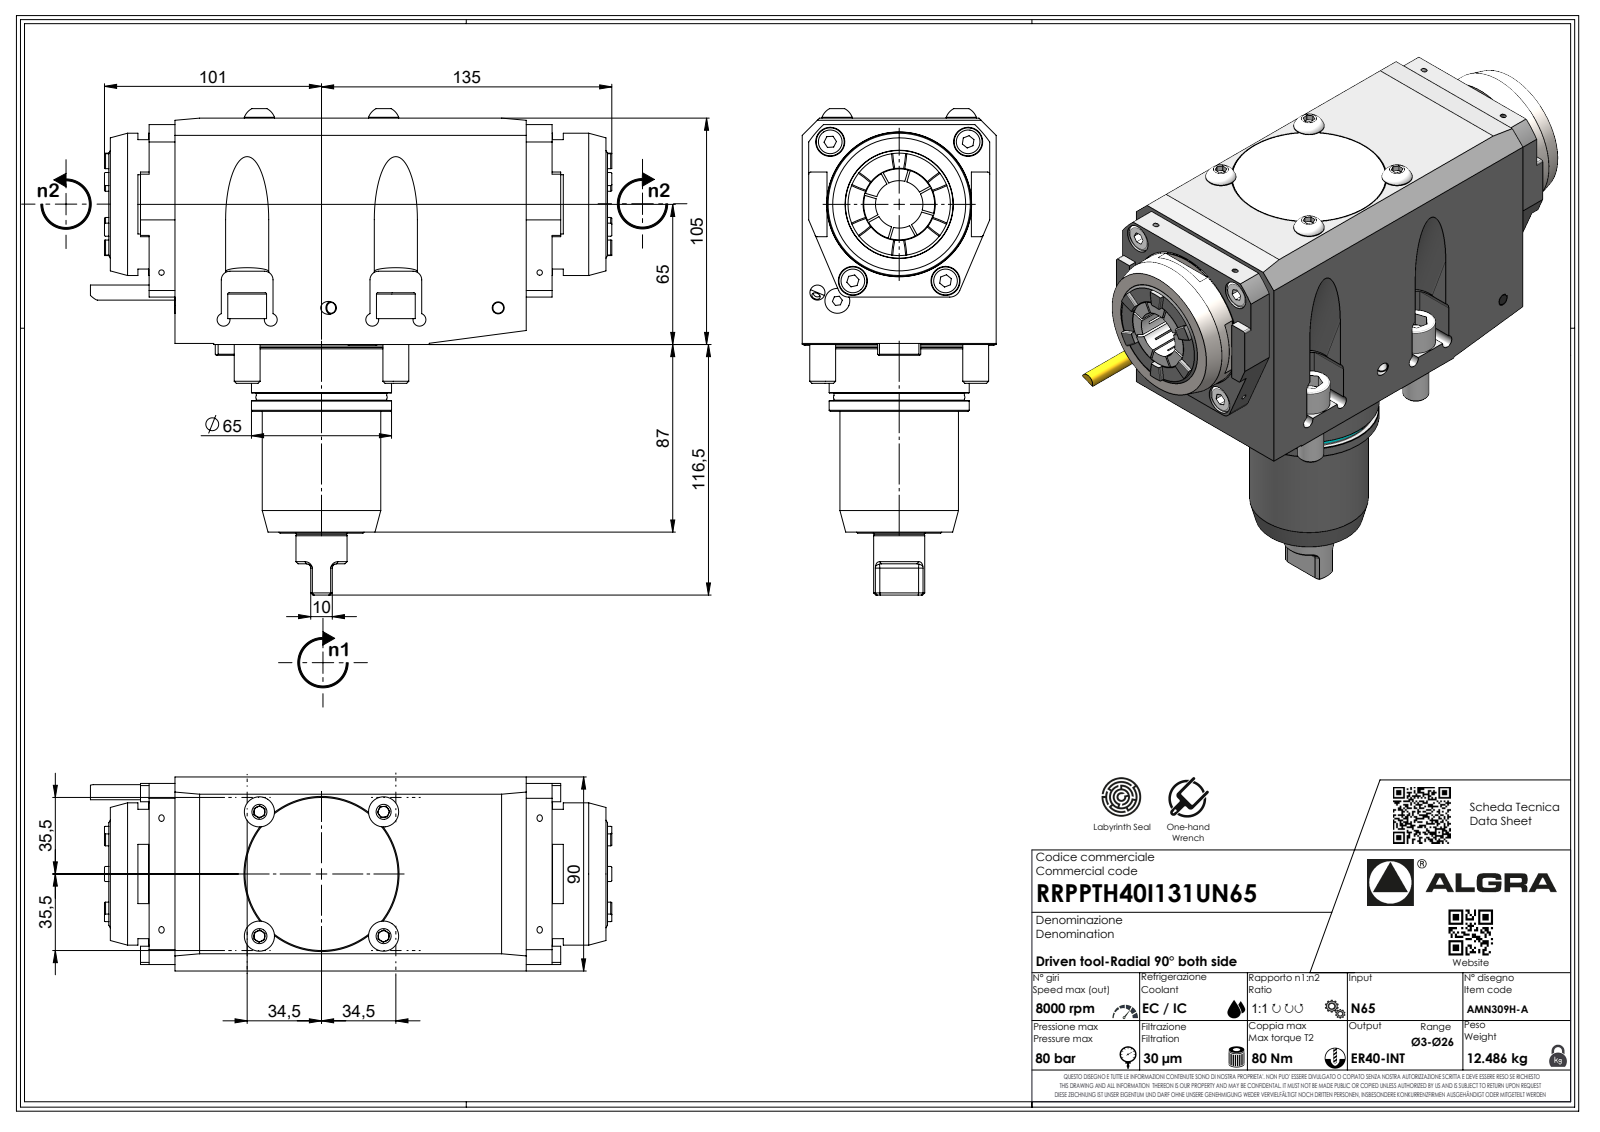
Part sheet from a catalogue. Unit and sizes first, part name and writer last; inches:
Units: inches
Overall size (bounding box): 9.055 × 8.709 × 3.543
Round holes (diameter × count): ⌀0.083 ×1
Round bosses / shafts (diameter × count): ⌀0.472 ×4, ⌀2.598 ×1, ⌀2.559 ×1, ⌀2.543 ×1, ⌀2.382 ×1, ⌀2.165 ×1, ⌀0.933 ×1, ⌀0.251 ×1
Partial cylindrical surfaces — rounded edges, fillets, slot ends (radius × count): R0.118 ×8, R0.013 ×7, R0.02 ×7, R0.146 ×7, R0.079 ×6, R0.039 ×4, R0.197 ×2, R0.008 ×1
Main face-to-face distances: 3.543, 0.472, 4.134, 6.89, 0.118, 1.181, 7.874, 9.055, 3.425, 0.709
Volume: 125.3 in³ · Surface area: 186.3 in²
Bodies: 1 solid, 524 faces (349 planar, 76 cylindrical, 99 other)
Part name (STEP PRODUCT): RRPPTH40I131UN65
STEP written by: SolidWorks 2023 (AUTOMOTIVE_DESIGN)
